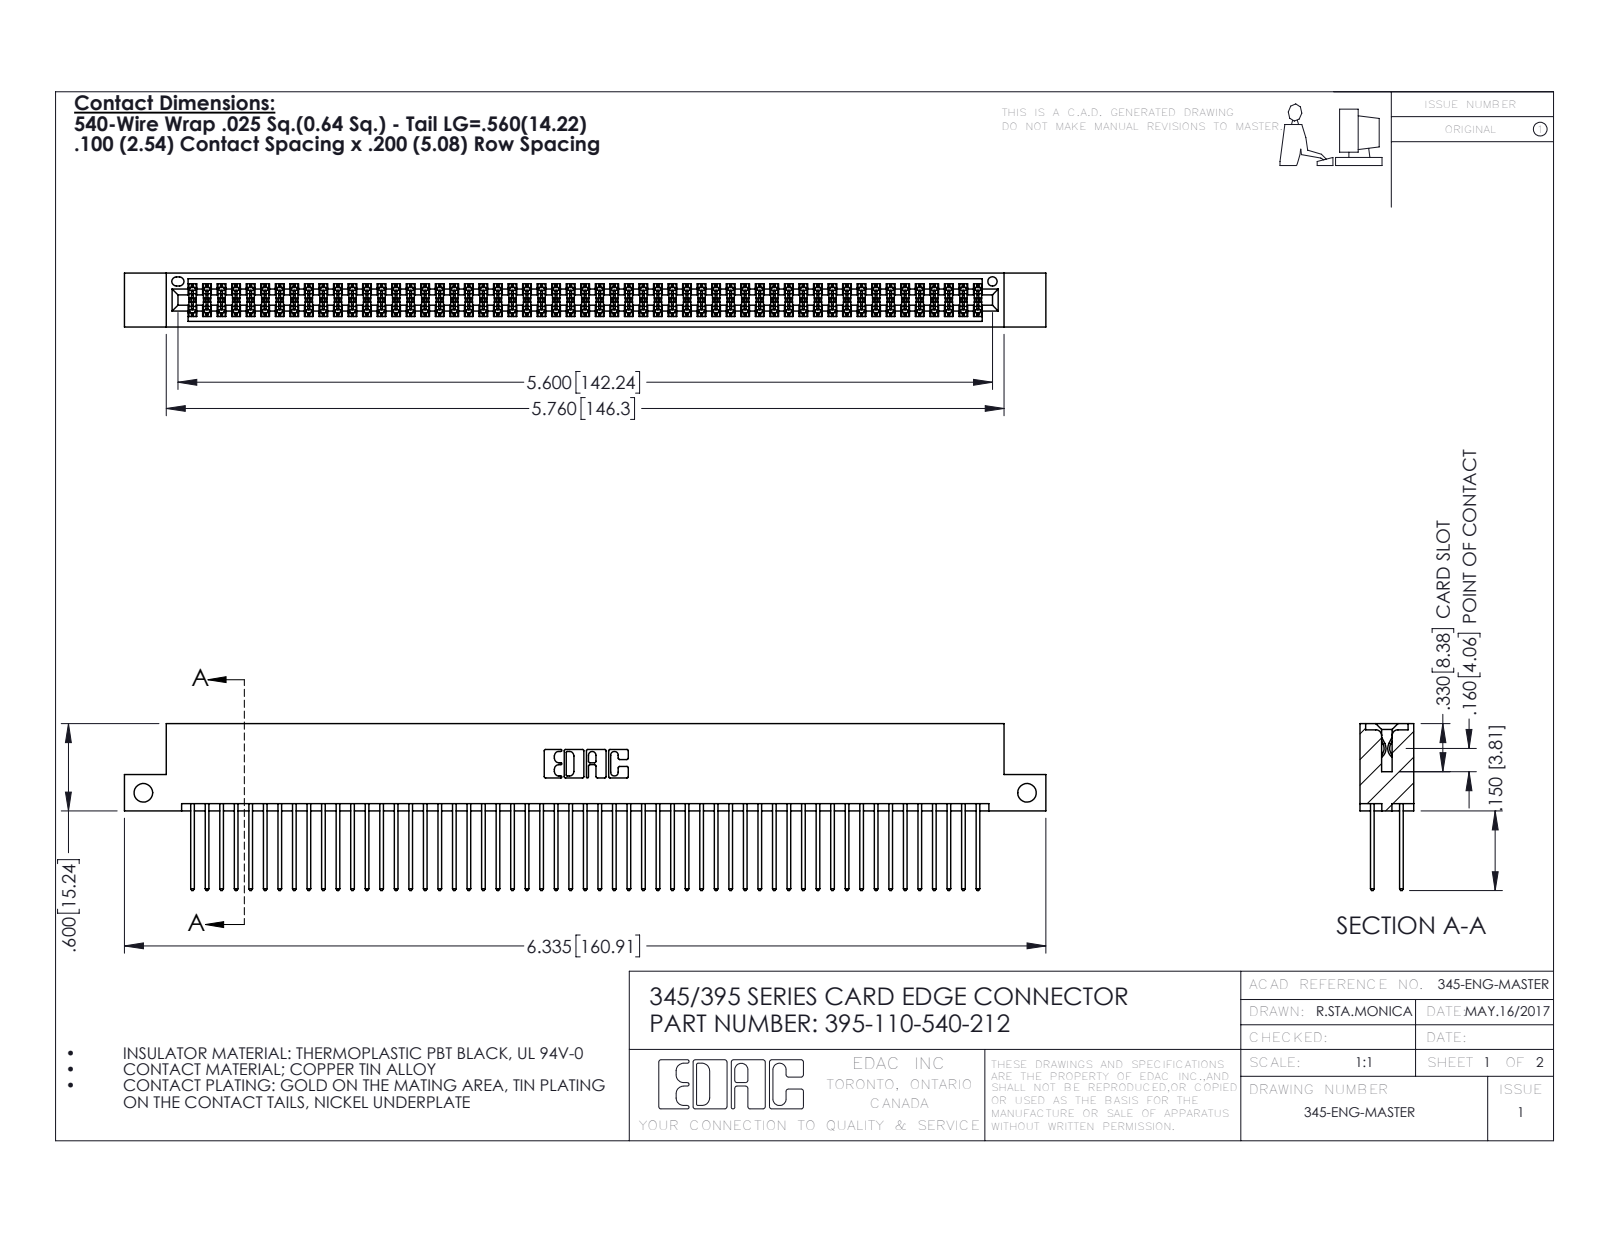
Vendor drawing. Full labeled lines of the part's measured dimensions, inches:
Part name (STEP PRODUCT): 345 Part_Flush Mounting Lugs - Side Mount; 345-292-001_345-293-140; 395-110-540-212
STEP written by: SolidWorks 2016 (CONFIG_CONTROL_DESIGN)
Units: inches
Bodies: 111 solids, 5626 faces (3710 planar, 1916 cylindrical, 0 other)
Overall size (bounding box): 6.335 × 1.147 × 0.37
Volume: 0.981 in³ · Surface area: 40.02 in²
Round holes (diameter × count): ⌀0.128 ×2, ⌀0.064 ×1
Partial cylindrical surfaces — rounded edges, fillets, slot ends (radius × count): R0.006 ×165, R0.01 ×110, R0.01 ×22, R0.007 ×6, R0.031 ×6, R0.026 ×3, R0.014 ×2, R0.019 ×2
Main face-to-face distances: 0.298, 0.072, 0.2, 0.098, 0.272, 0.025, 0.37, 0.225, 0.175, 0.149
Hole centre spacings: 6.075
